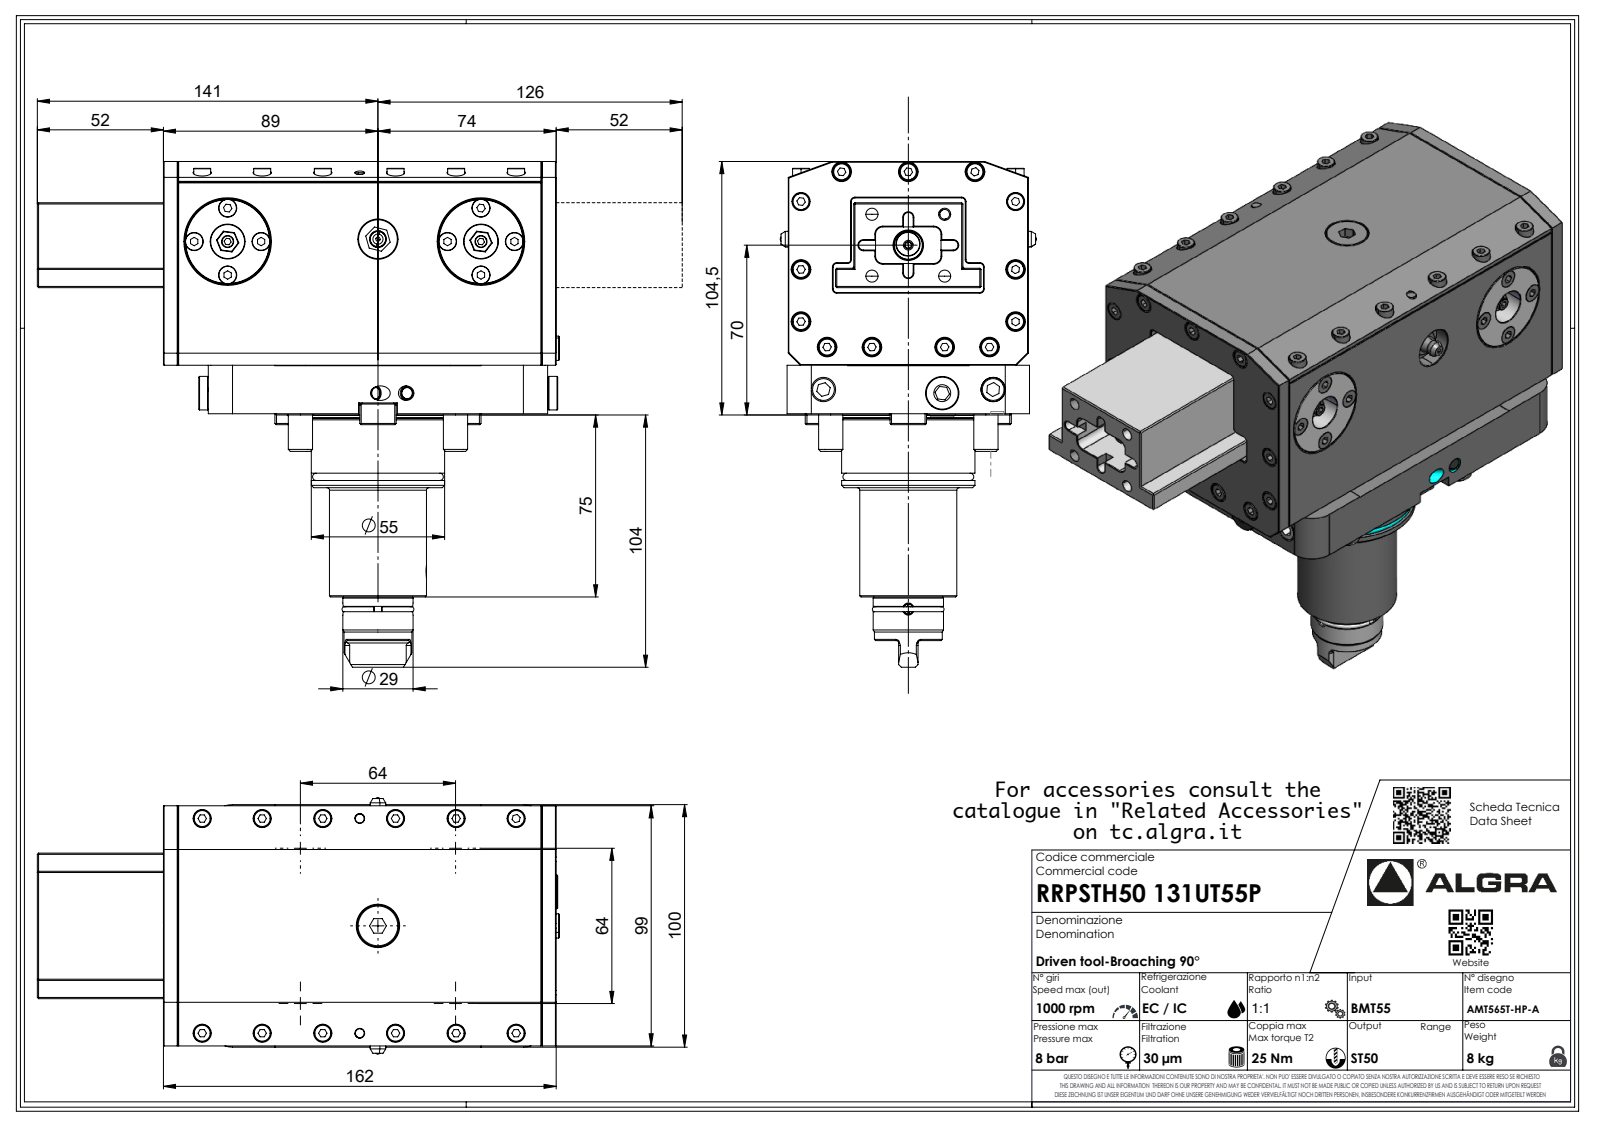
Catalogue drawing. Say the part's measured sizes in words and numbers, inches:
The part is named "RRPSTH50131UT55P". Its 3-D file was written by "SolidWorks 2023 (AUTOMOTIVE_DESIGN)". It is 1 solid with 797 faces: 519 planar, 118 cylindrical and 160 other. Overall it measures 8.478 by 8.209 by 4.157 inches. Its volume is 112 cubic inches and its surface area 196.2 square inches. Round holes: 1 of diameter 0.083, 1 of diameter 0.197, 1 of diameter 2.402. Round bosses or shafts: 12 of diameter 0.276, 1 of diameter 2.165, 1 of diameter 2.15, 1 of diameter 1.976, 1 of diameter 1.575, 1 of diameter 1.142, 1 of diameter 1.102, 1 of diameter 0.394. Partial cylindrical surfaces (rounded edges, fillets, slot ends): 12 of radius 0.098, 8 of radius 0.394, 7 of radius 0.013, 7 of radius 0.02, 7 of radius 0.146, 6 of radius 0.079, 4 of radius 0.118, 4 of radius 0.315. The main face-to-face distances are 3.898, 3.307, 0.02, 0.787, 3.315, 2.047, 4.094, 0.78, 6.378, 3.917. The hole center spacings are 2.176.
